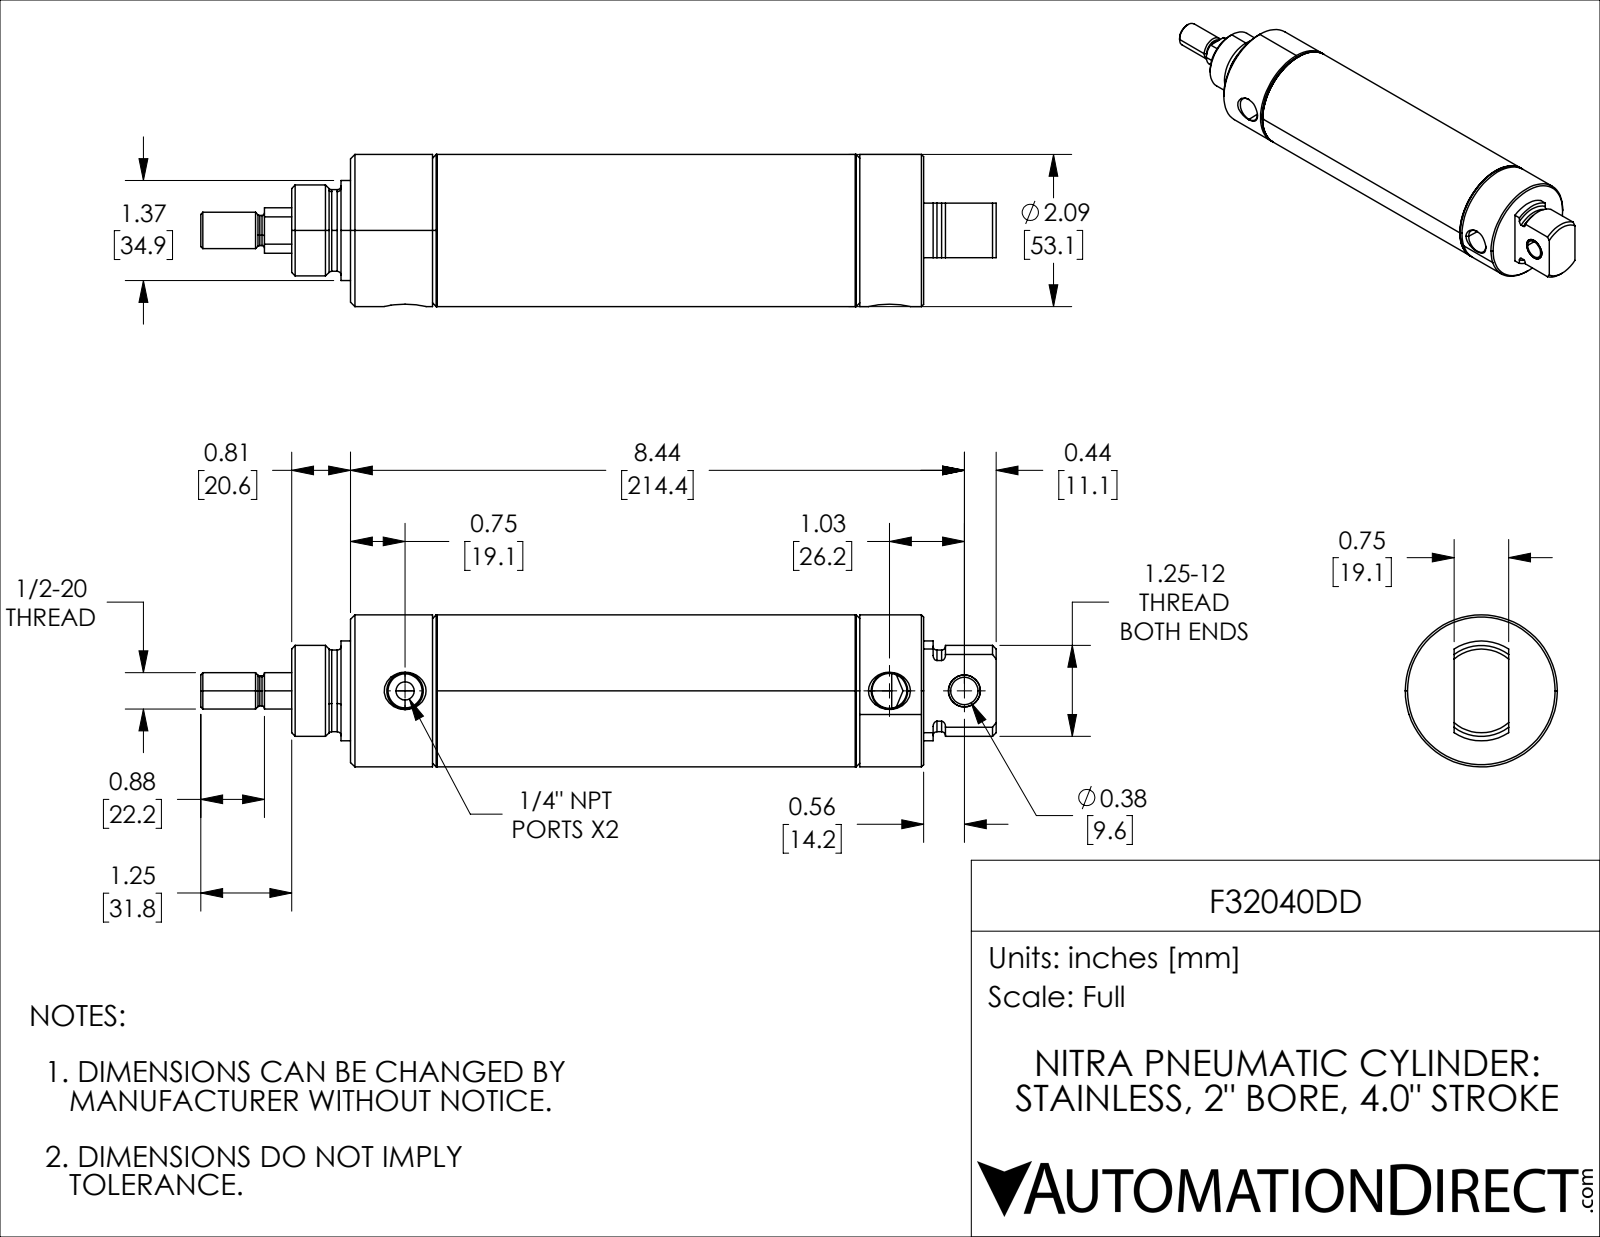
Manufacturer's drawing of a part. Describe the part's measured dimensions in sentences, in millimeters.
The part is named "F32040DD; F32040DD_5; F32040DD_7; F32040DD_11 (+2 more)". Its 3-D file was written by "SolidWorks 2021 (CONFIG_CONTROL_DESIGN)". It is 5 solids with 160 faces: 31 planar, 60 cylindrical and 69 other. Overall it measures 277.82 by 53.09 by 53.09 millimeters. Its volume is 271 929 cubic millimeters and its surface area 100 392 square millimeters. Round holes: 1 of diameter 6.35, 1 of diameter 9.55, 1 of diameter 11.15, 1 of diameter 12.18, 1 of diameter 16.52, 1 of diameter 19.05, 1 of diameter 49.05. Round bosses or shafts: 1 of diameter 53.09, 1 of diameter 51.16, 1 of diameter 34.87, 1 of diameter 31.75, 1 of diameter 28.51, 1 of diameter 15.88, 1 of diameter 12.7, 1 of diameter 10.46. Partial cylindrical surfaces (rounded edges, fillets, slot ends): 1 of radius 14.25. The main face-to-face distances are 30.18, 101.6, 131.78, 162, 60.4, 30.22, 131.77, 30.17, 30.23, 38.15. The hole center spacings are 26.16, 169.16, 195.32.
